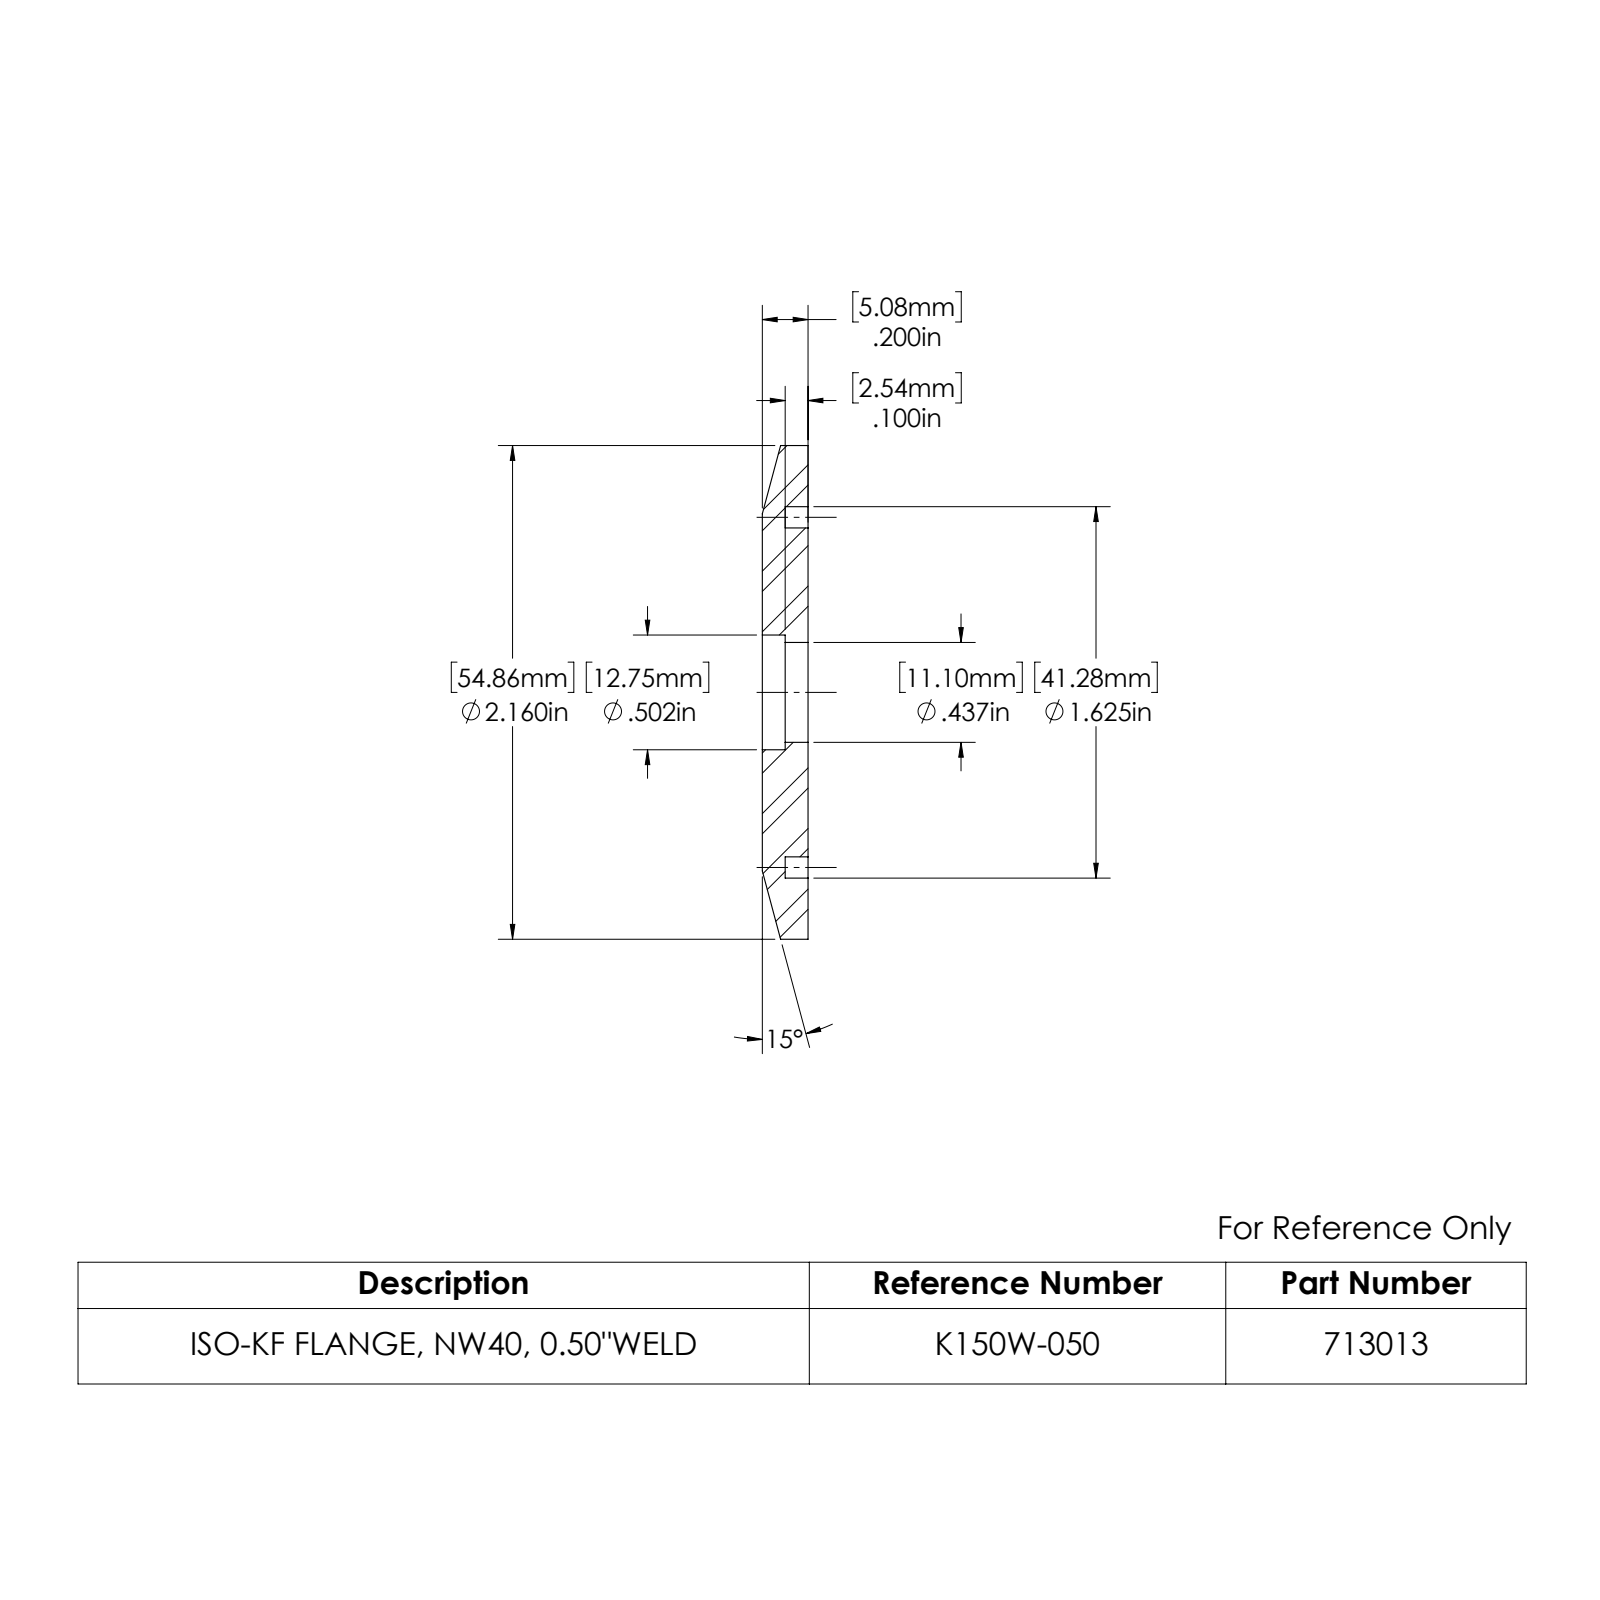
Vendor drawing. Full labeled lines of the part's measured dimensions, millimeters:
Part name (STEP PRODUCT): 713013
STEP written by: SolidWorks 2022 (AUTOMOTIVE_DESIGN)
Units: millimetres
Bodies: 1 solid, 17 faces (5 planar, 10 cylindrical, 2 other)
Overall size (bounding box): 54.9 × 54.9 × 5.1
Volume: 9 500 mm³ · Surface area: 5 911 mm²
Round holes (diameter × count): ⌀11.1 ×1, ⌀12.8 ×1, ⌀41.3 ×1
Round bosses / shafts (diameter × count): ⌀54.9 ×1, ⌀36.6 ×1
Main face-to-face distances: 5.1, 2.5
